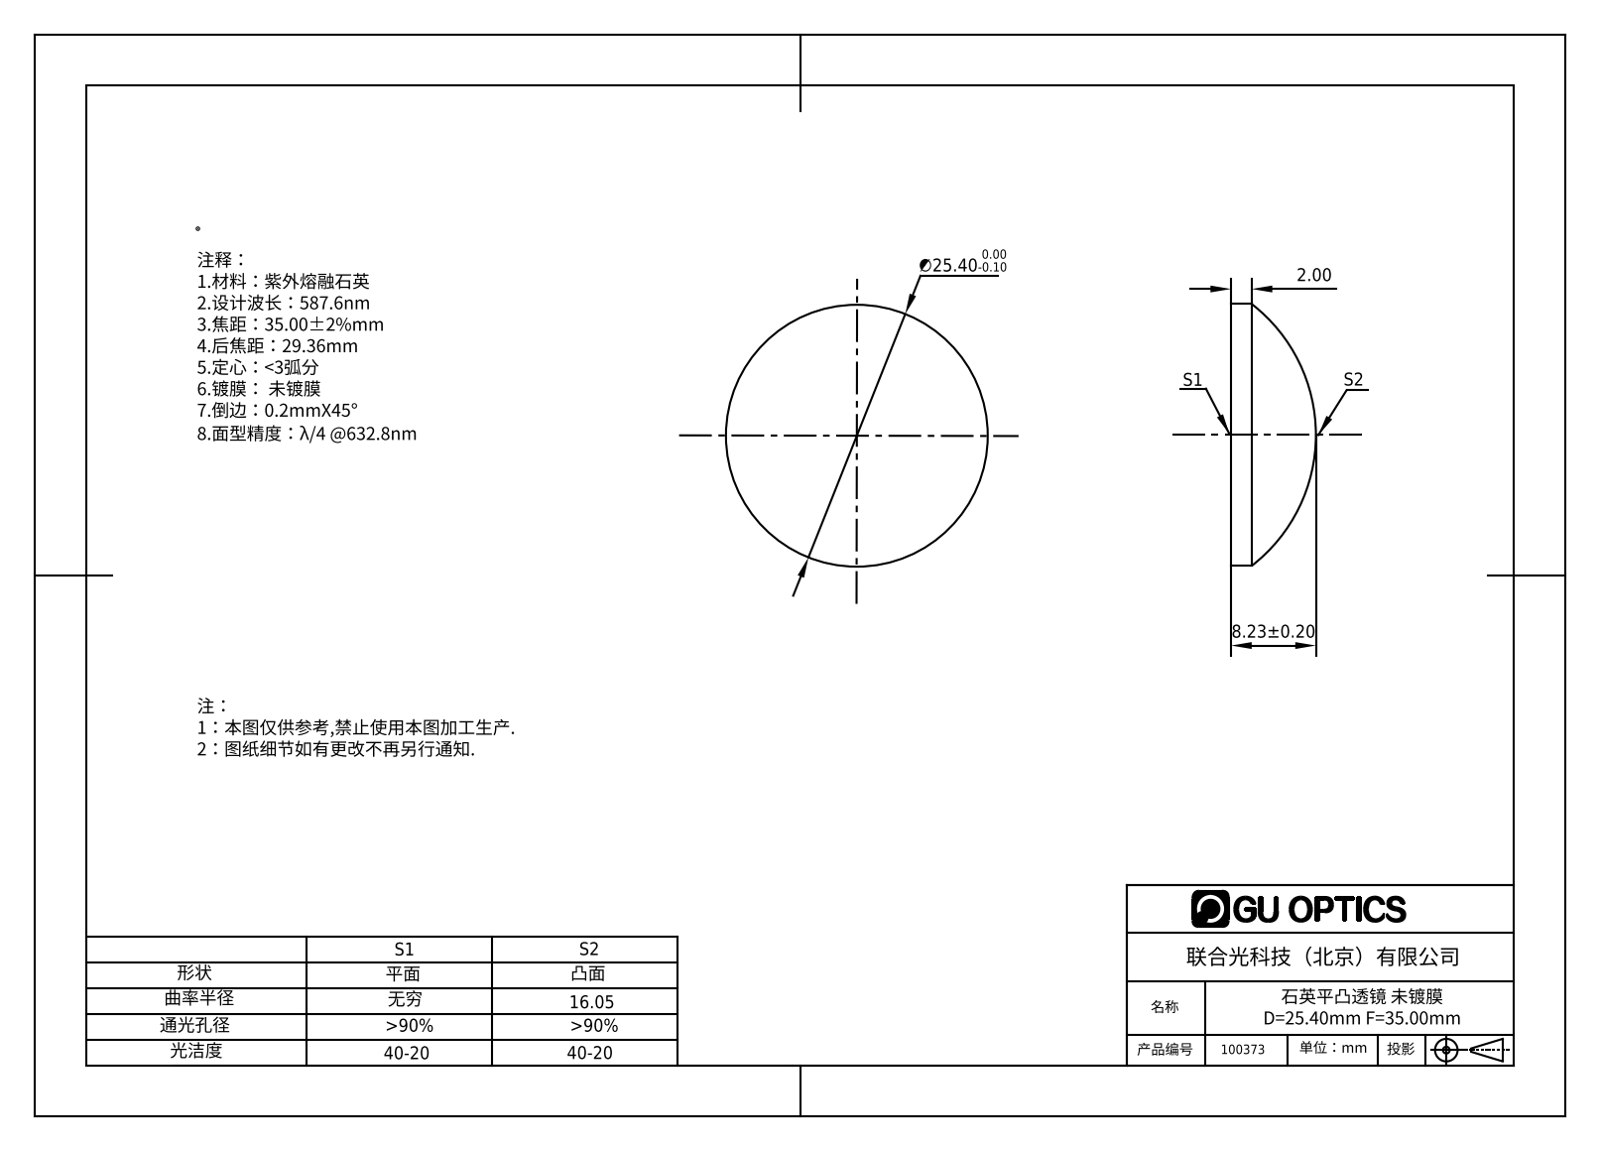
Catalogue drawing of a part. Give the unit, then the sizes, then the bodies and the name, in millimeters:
Units: millimetres
Overall size (bounding box): 25.4 × 25.4 × 8.23
Round bosses / shafts (diameter × count): ⌀25.4 ×1
Volume: 2 718 mm³ · Surface area: 1 295 mm²
Bodies: 1 solid, 5 faces (1 planar, 2 cylindrical, 2 other)
Part name (STEP PRODUCT): 100373
STEP written by: SolidWorks 2016 (AUTOMOTIVE_DESIGN)
